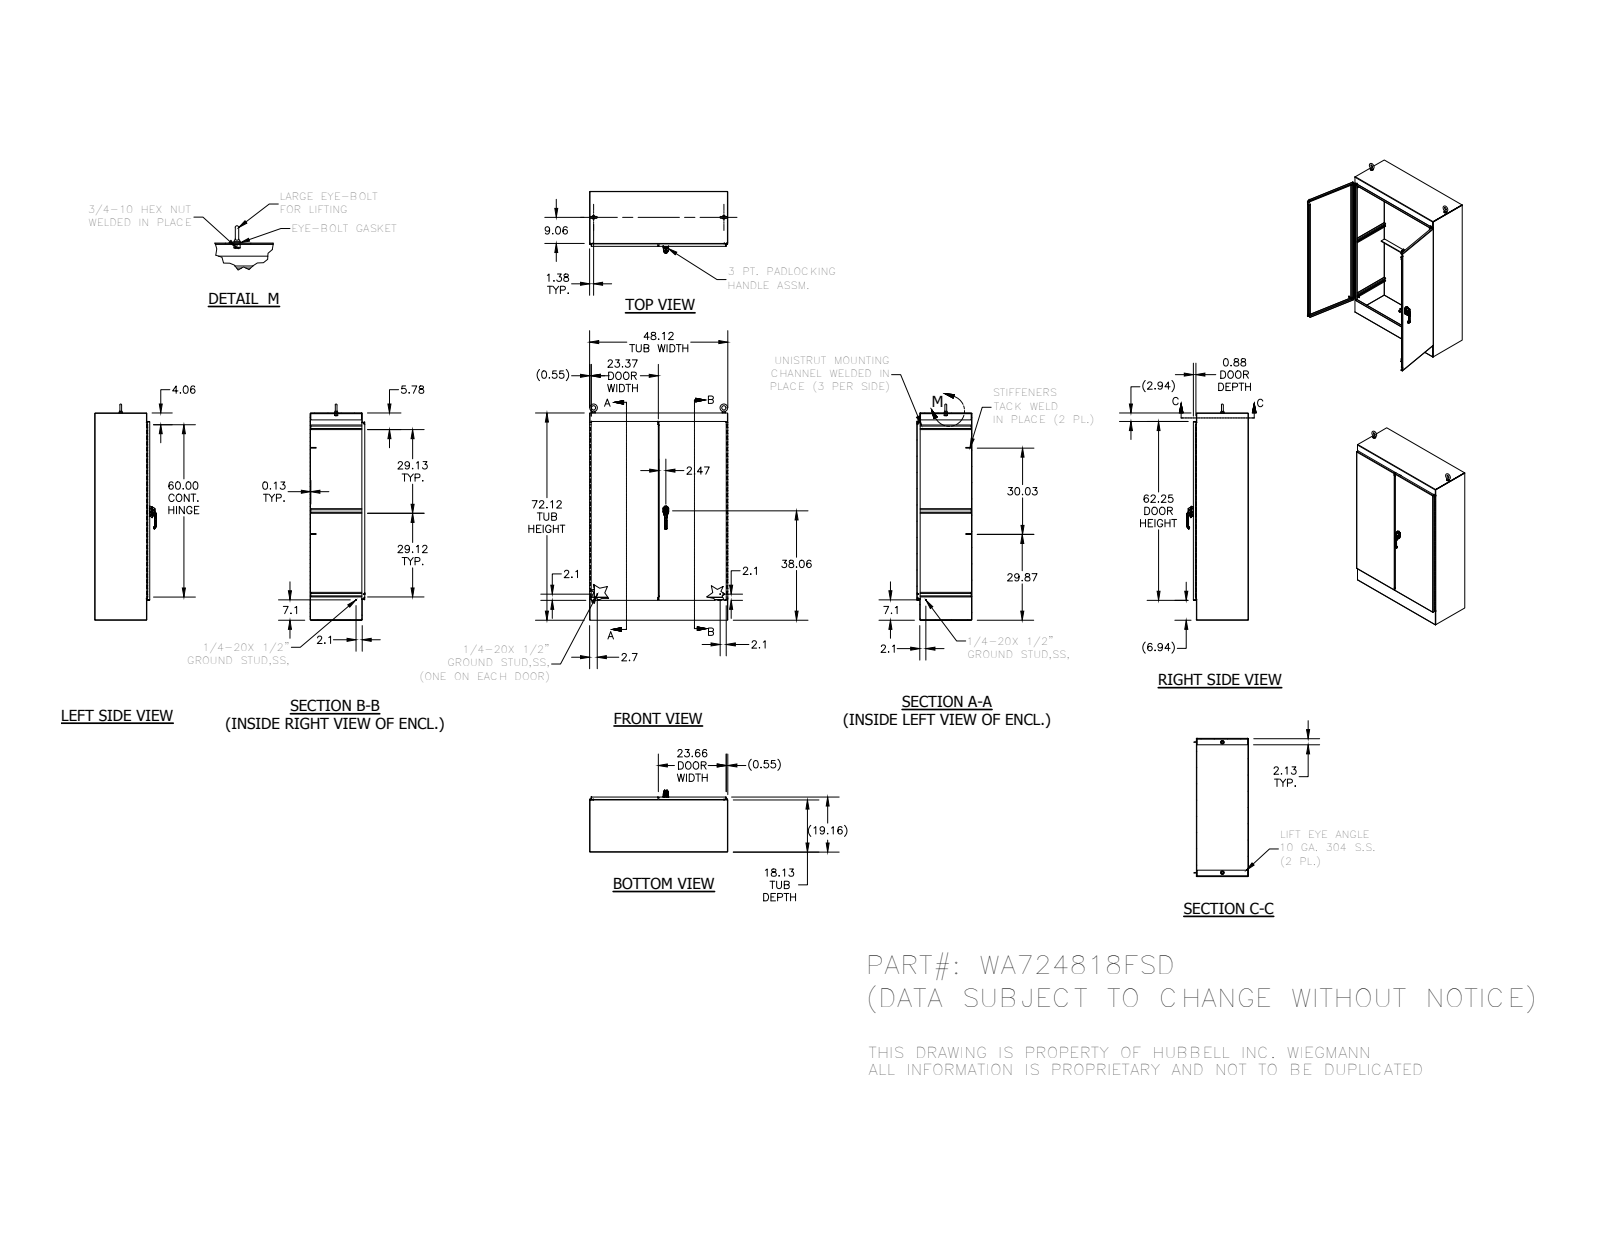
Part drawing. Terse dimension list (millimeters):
name: FUN00101; HFW3025; 316298; 349132 (+8 more)
written by: Autodesk Inventor 2014 (AUTOMOTIVE_DESIGN)
unit: mm
bodies: 66 solids, 3780 faces (1777 planar, 1263 cylindrical, 740 other)
size: 1911.29 × 1222.74 × 544.36
volume: 27 560 000 mm³; area: 17 450 000 mm²
holes: 8× ⌀7.02, 4× ⌀5.08, 3× ⌀5.4, 3× ⌀6, 3× ⌀7.11, 2× ⌀3.17, 2× ⌀6.13, 2× ⌀6.35, 2× ⌀6.41, 2× ⌀10.16, 2× ⌀10.33, 2× ⌀10.5
bosses: 5× ⌀6.35, 3× ⌀8.56, 2× ⌀31.75, 2× ⌀28.45, 2× ⌀25.4, 2× ⌀19.05, 2× ⌀14.29, 2× ⌀13.37
rounds: 164× R0.5, 84× R0.3, 24× R0.79, 21× R3.97, 19× R0.47, 16× R0.25, 15× R2, 14× R1.27
face distances: 3.18, 3.17, 483.57, 480.39, 486.74, 483.56, 1219.2, 1828.8, 1216.02, 457.2
hole spacings: 6, 6.5, 9.67, 9.69, 9.72, 12.49, 12.5, 19.36
